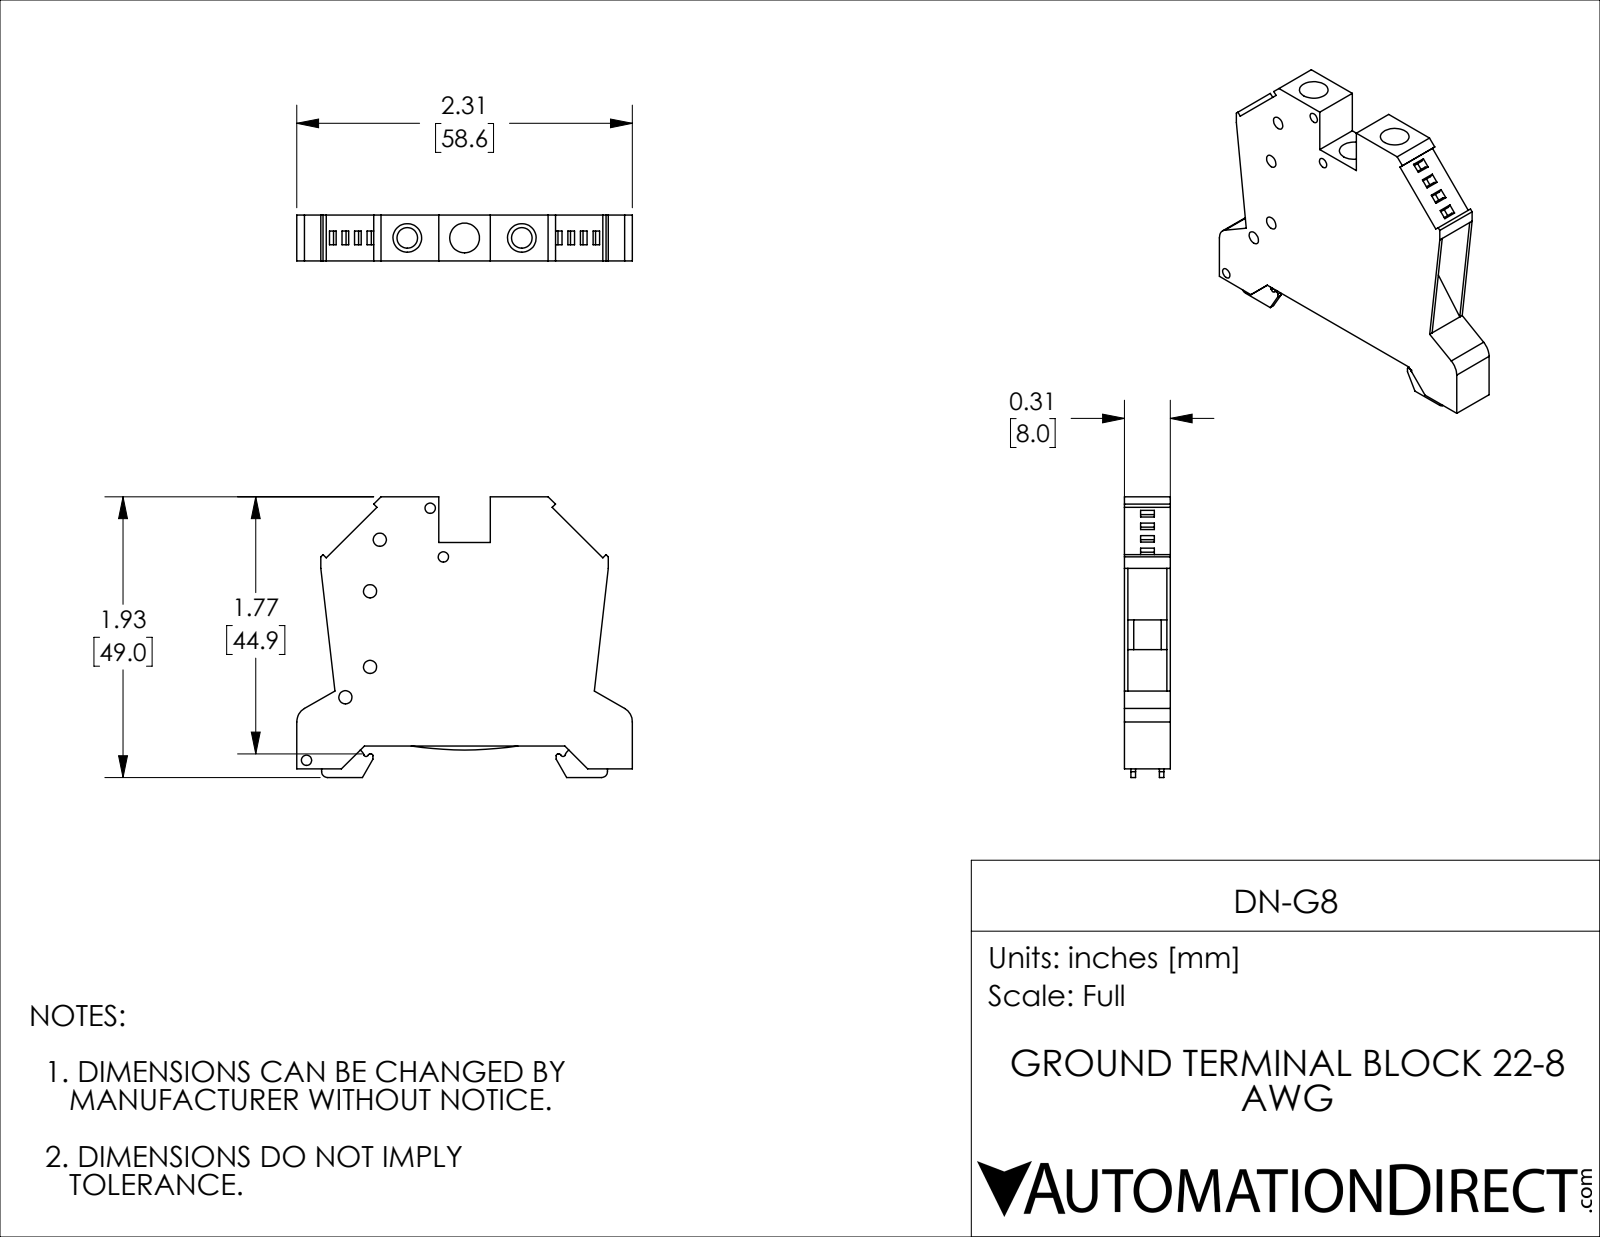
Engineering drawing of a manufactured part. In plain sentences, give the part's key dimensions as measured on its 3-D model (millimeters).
The part is named "43450_DN-G8; 20515A". Its 3-D file was written by "SolidWorks 2013 (AUTOMOTIVE_DESIGN)". It is 1 solid with 407 faces: 209 planar, 144 cylindrical and 54 other. Overall it measures 58.6 by 49 by 8 millimeters. Its volume is 14 409 cubic millimeters and its surface area 7 798 square millimeters. Round holes: 8 of diameter 2.3, 6 of diameter 1.6, 6 of diameter 1.8, 2 of diameter 2.1, 2 of diameter 3.6, 2 of diameter 5, 1 of diameter 5.2. Round bosses or shafts: 6 of diameter 1.2, 2 of diameter 1.7. Partial cylindrical surfaces (rounded edges, fillets, slot ends): 4 of radius 0.3, 2 of radius 0.4, 2 of radius 0.85, 2 of radius 1, 2 of radius 1.05, 2 of radius 1.7, 2 of radius 2.7, 1 of radius 62. The main face-to-face distances are 8, 0.6, 7.4, 6.8, 0.8, 2.2, 4, 24.8, 33.8, 43.5. The hole center spacings are 6.82, 8.81, 9.16, 10, 10.38, 11.5, 12.9, 12.93.
